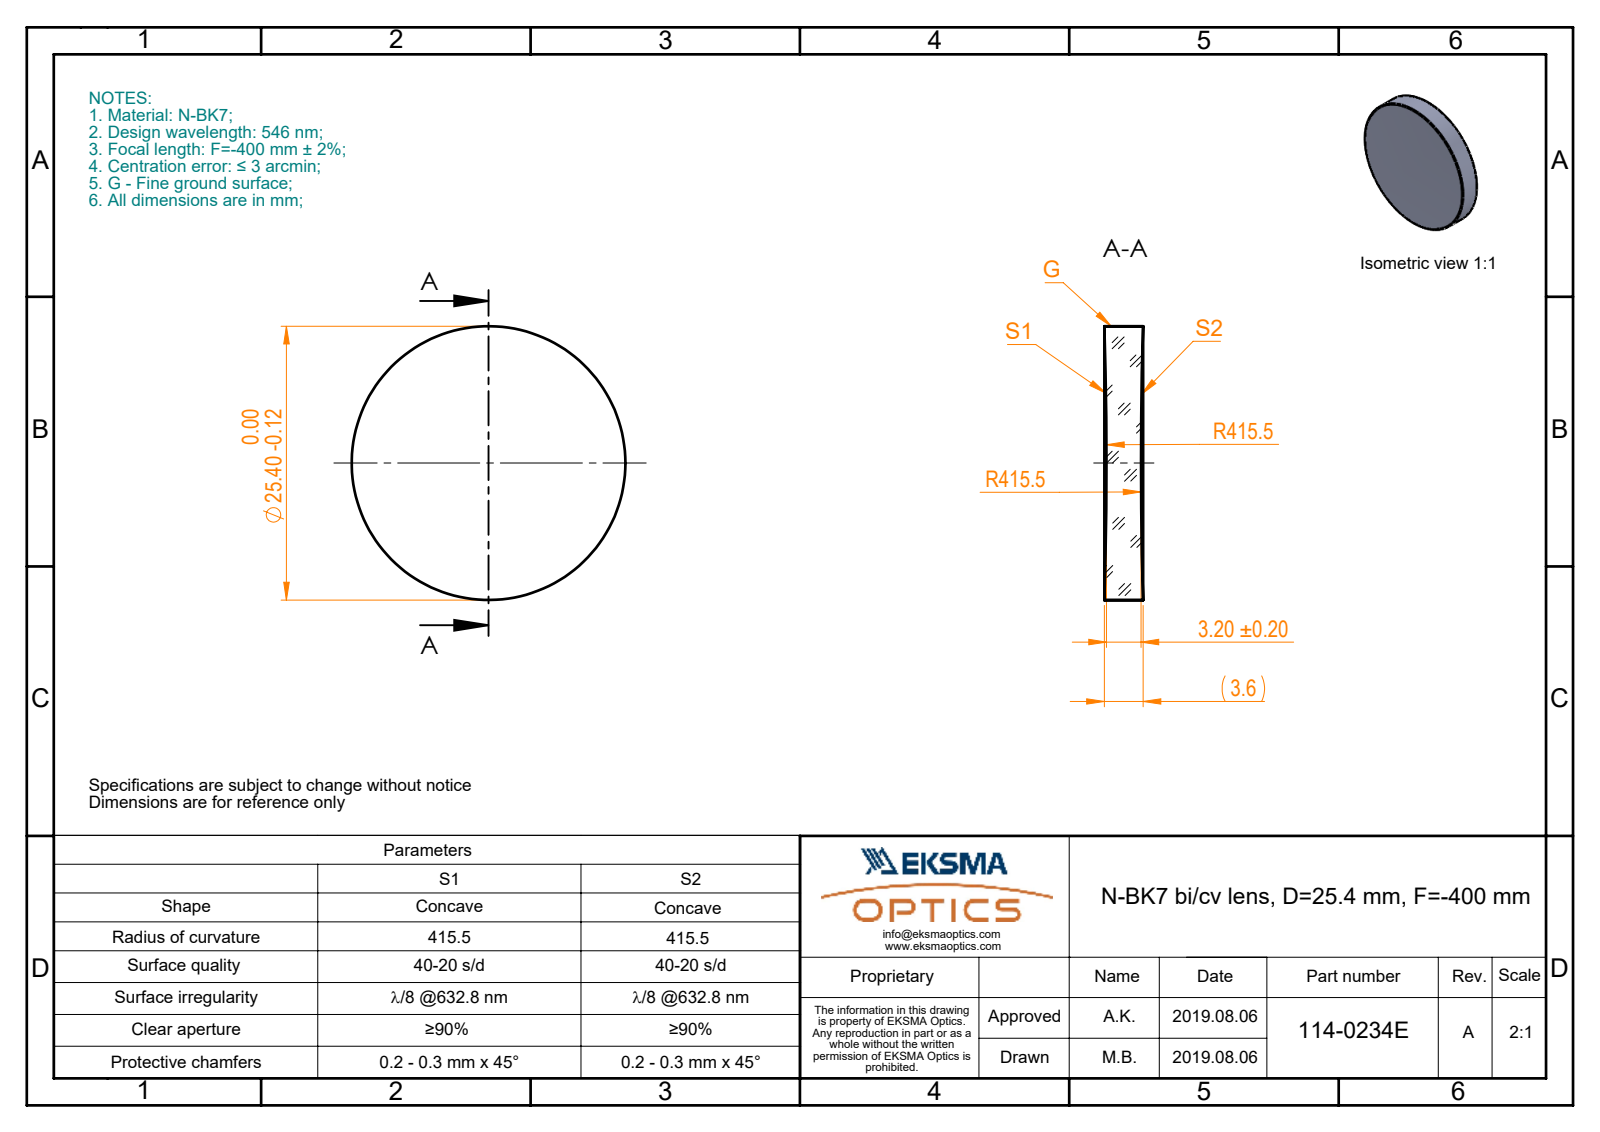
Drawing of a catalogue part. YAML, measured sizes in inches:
part_name: "114-0234E BK7 bi-cv 25.4 F-400"
step_written_by: "SolidWorks 2017 (CONFIG_CONTROL_DESIGN)"
units: inches
bodies: {solids: 1, faces: 6, planar: 0, cylindrical: 2, other: 4}
overall_size: [1, 1, 0.141]
volume: 0.105
surface_area: 2.015
round_bosses_or_shafts:
  - {diameter: 1, count: 1}
